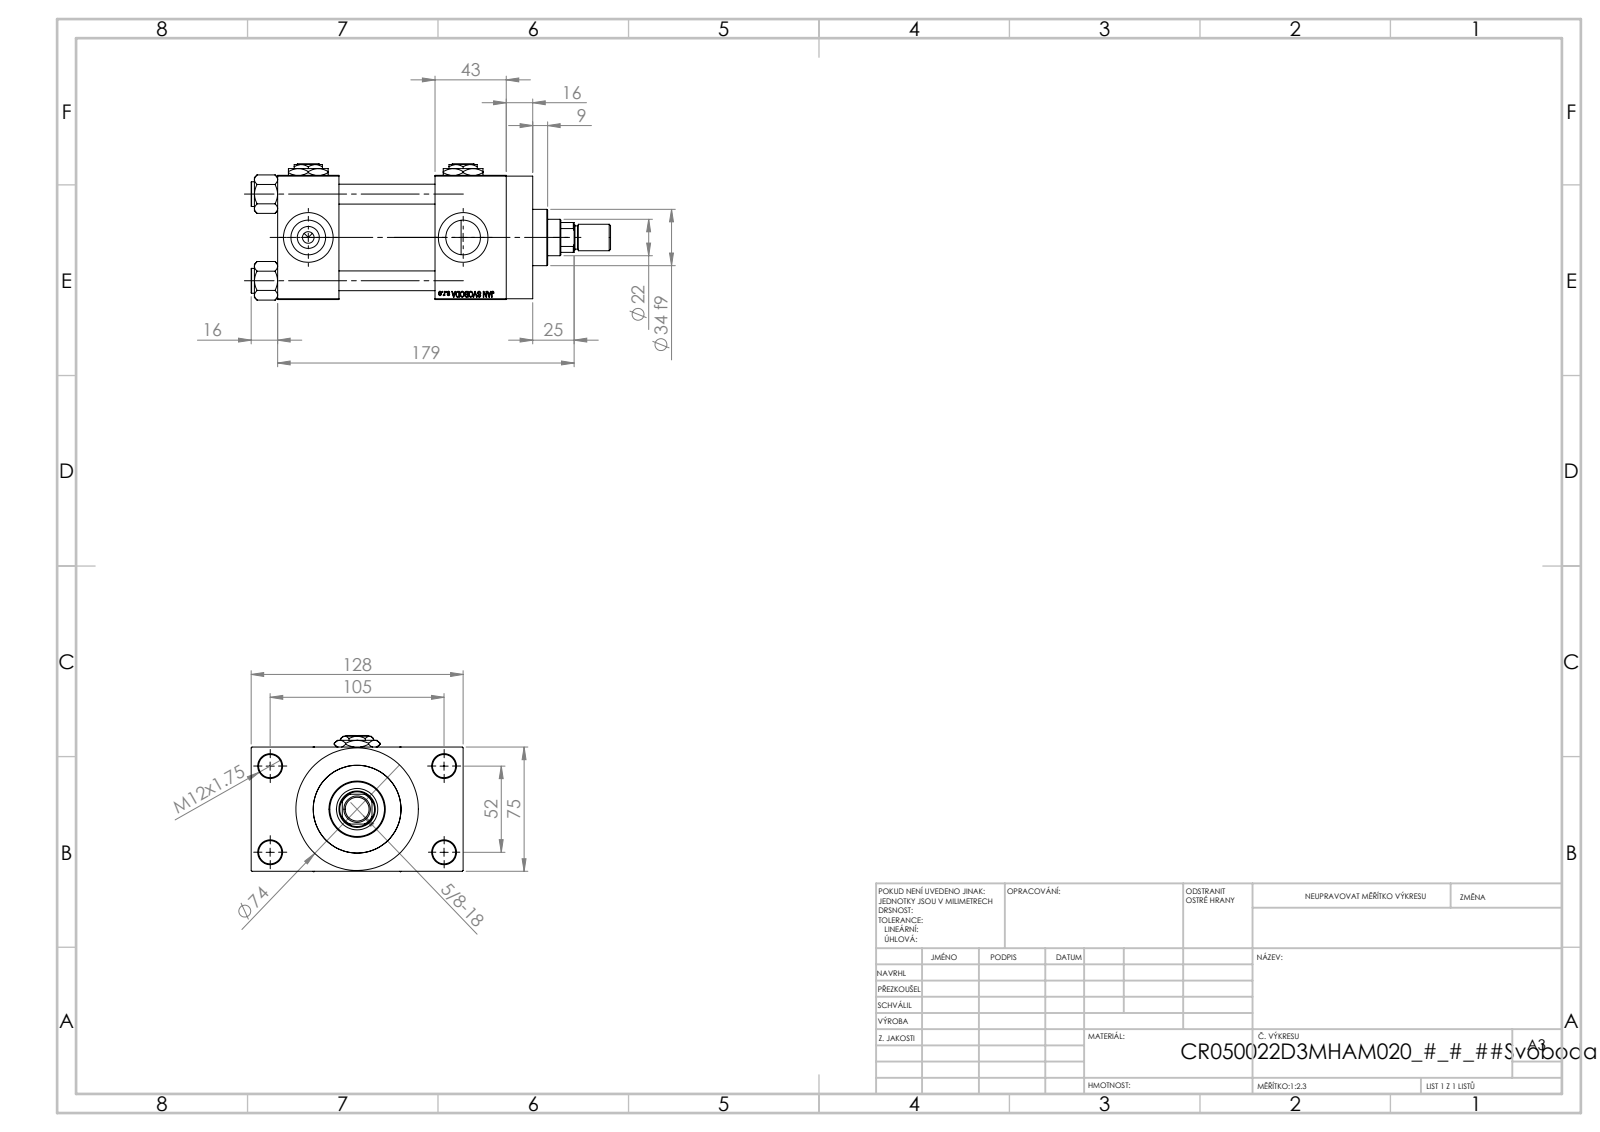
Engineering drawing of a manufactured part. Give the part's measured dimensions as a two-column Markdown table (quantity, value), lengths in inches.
| quantity | value |
| --- | --- |
| part name | V215CR_D_TYCINKA; ROD_END_AH; Zatka_pro_OIL_PORT; V215_VC_A (+3 more) |
| STEP written by | SolidWorks 2019 (CONFIG_CONTROL_DESIGN) |
| units | inches |
| bodies | 14 solids, 1218 faces (549 planar, 103 cylindrical, 566 other) |
| overall size | 8.543 × 5.039 × 3.239 |
| volume | 48.66 in³ |
| surface area | 267.3 in² |
| round holes (diameter × count) | 0.472 × 4, 0.551 × 4, 0.825 × 4, 1.181 × 4, 0.276 × 3, 0.413 × 1, 0.866 × 1, 0.984 × 1, 1.614 × 1, 1.969 × 1, 2.087 × 1 |
| round bosses / shafts (diameter × count) | 0.591 × 4, 2.913 × 1, 2.205 × 1, 1.339 × 1, 0.63 × 1, 0.551 × 1 |
| partial cylindrical surfaces (radius × count) | 0.413 × 1 |
| main face-to-face distances | 2.953, 2.283, 1.457, 3.74, 1.043, 3.976, 5.433, 1.693, 3.996, 0.63 |
| hole center spacings | 1.037, 1.456, 2.059, 2.3, 2.307, 3.096, 3.715, 2.047 |
